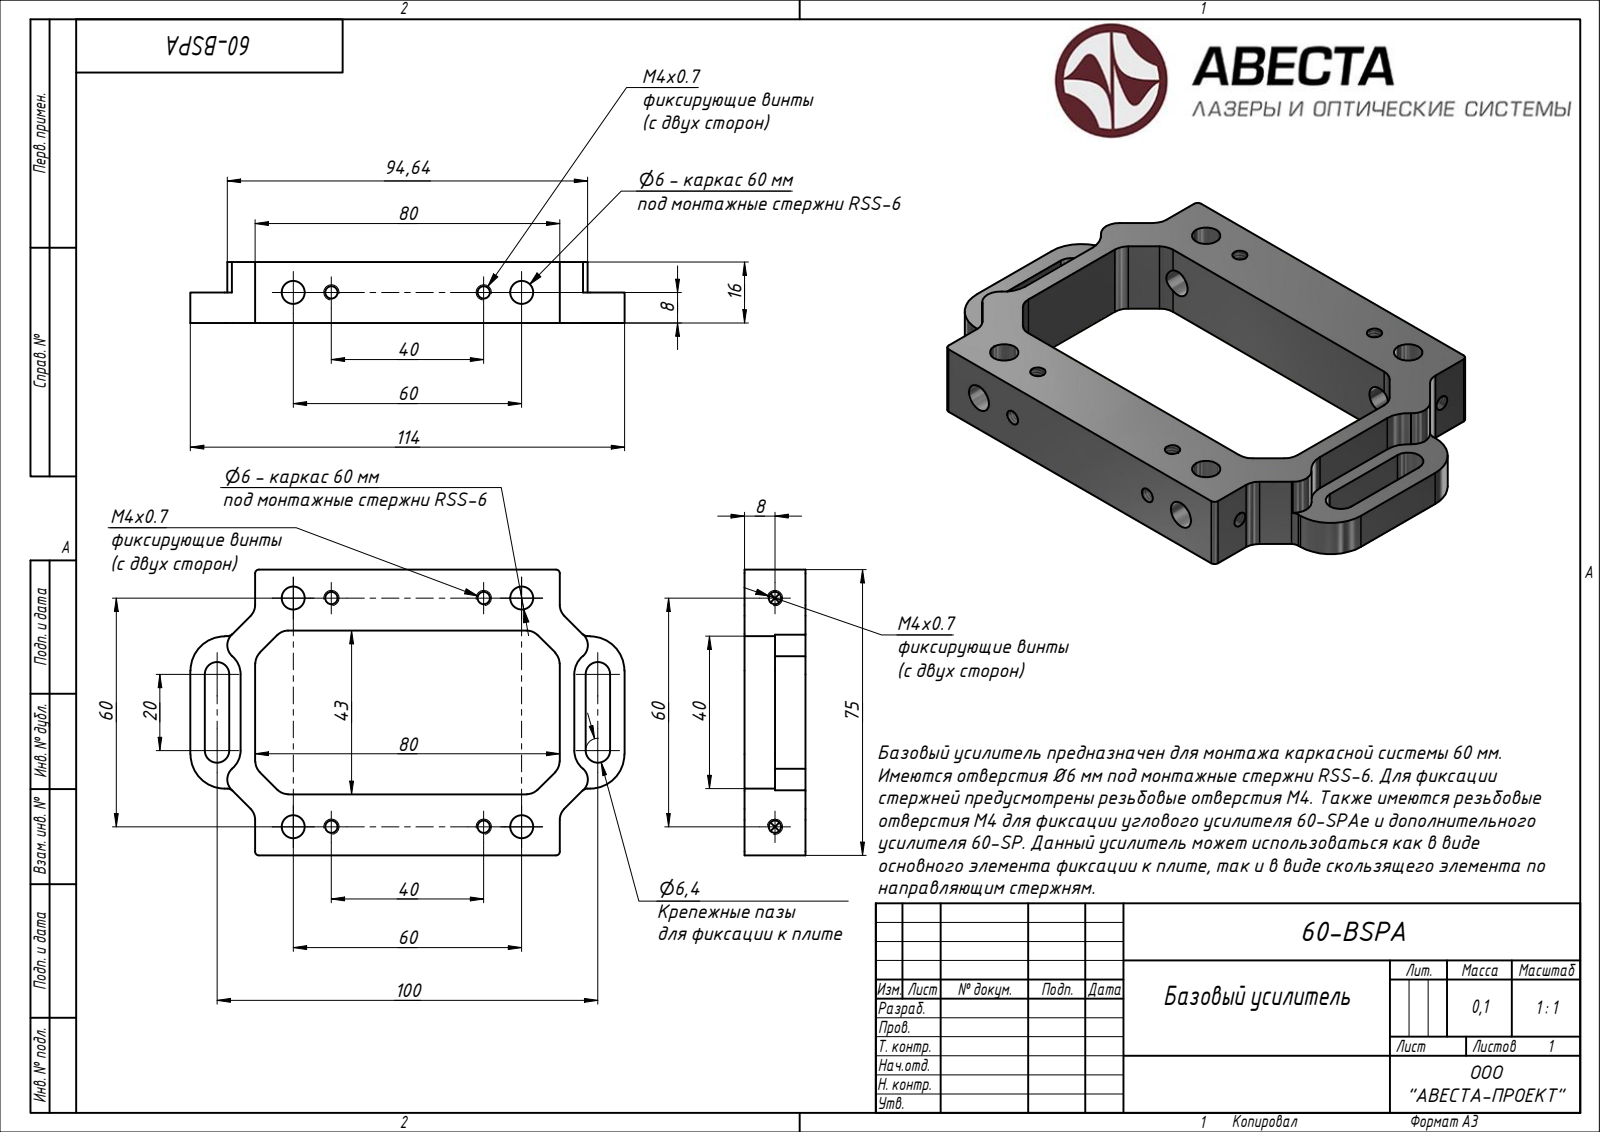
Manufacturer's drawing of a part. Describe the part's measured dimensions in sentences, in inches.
Its 3-D file was written by "ST-DEVELOPER v15 (AUTOMOTIVE_DESIGN)". It is 1 solid with 146 faces: 38 planar, 0 cylindrical and 108 other. Overall it measures 4.488 by 2.953 by 0.63 inches. Its volume is 3.095 cubic inches and its surface area 30.73 square inches. The main face-to-face distances are 0.63, 2.323, 2.953, 0.315, 1.693, 3.819, 3.15, 0.15, 0.52, 0.334.
